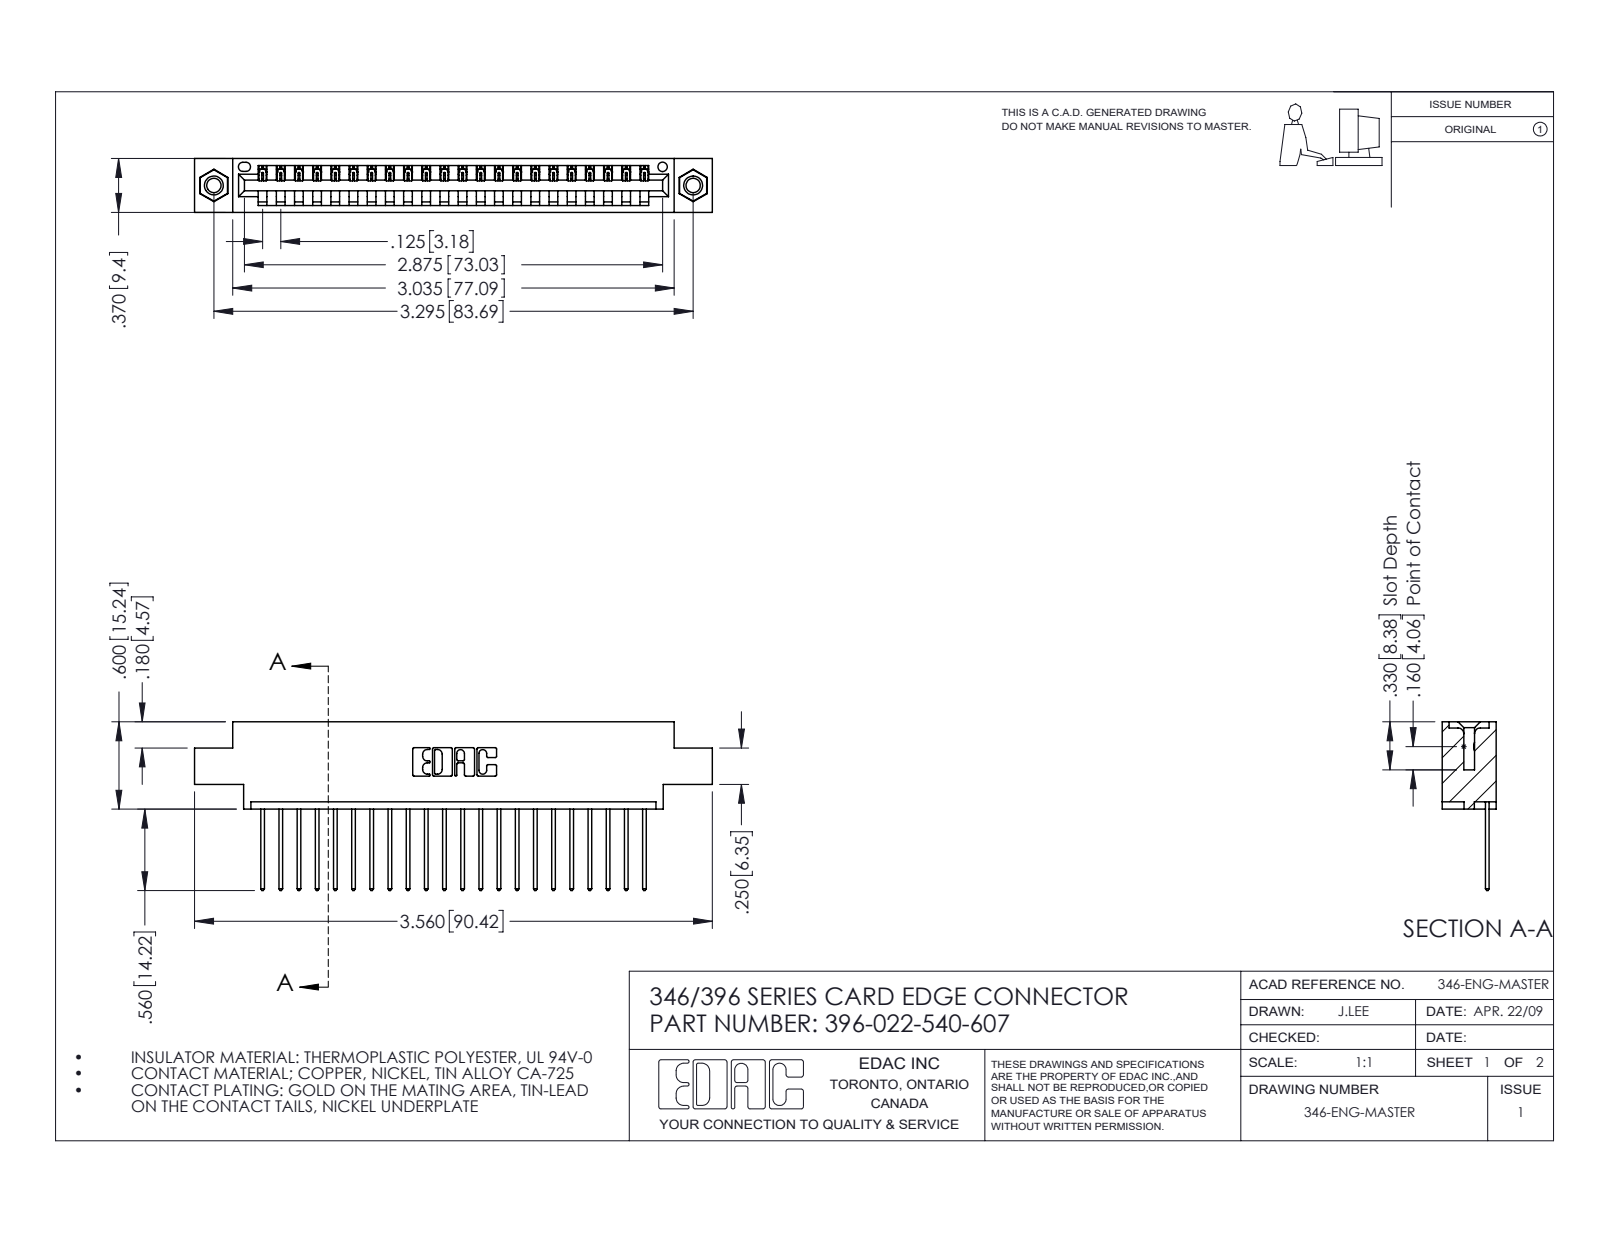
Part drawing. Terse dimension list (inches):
name: 346 Part_0.170 Offset - 0.156 Dia-TI; 345-292-001_345-293-140; 396-022-540-607; 345-250-001_345-250-005-103
written by: SolidWorks 2016 (CONFIG_CONTROL_DESIGN)
unit: in
bodies: 25 solids, 1462 faces (992 planar, 454 cylindrical, 16 other)
size: 3.56 × 1.16 × 0.37
volume: 0.511 in³; area: 16.54 in²
holes: 2× ⌀0.098, 2× ⌀0.125, 2× ⌀0.156, 1× ⌀0.064
bosses: 2× ⌀0.155
rounds: 44× R0.006, 44× R0.01, 22× R0.01, 6× R0.007, 6× R0.031, 3× R0.026, 2× R0.031, 2× R0.04
face distances: 0.048, 0.322, 0.37, 0.25, 0.072, 0.298, 0.025, 0.222, 0.148, 0.1
hole spacings: 0.246, 3.087, 3.295
